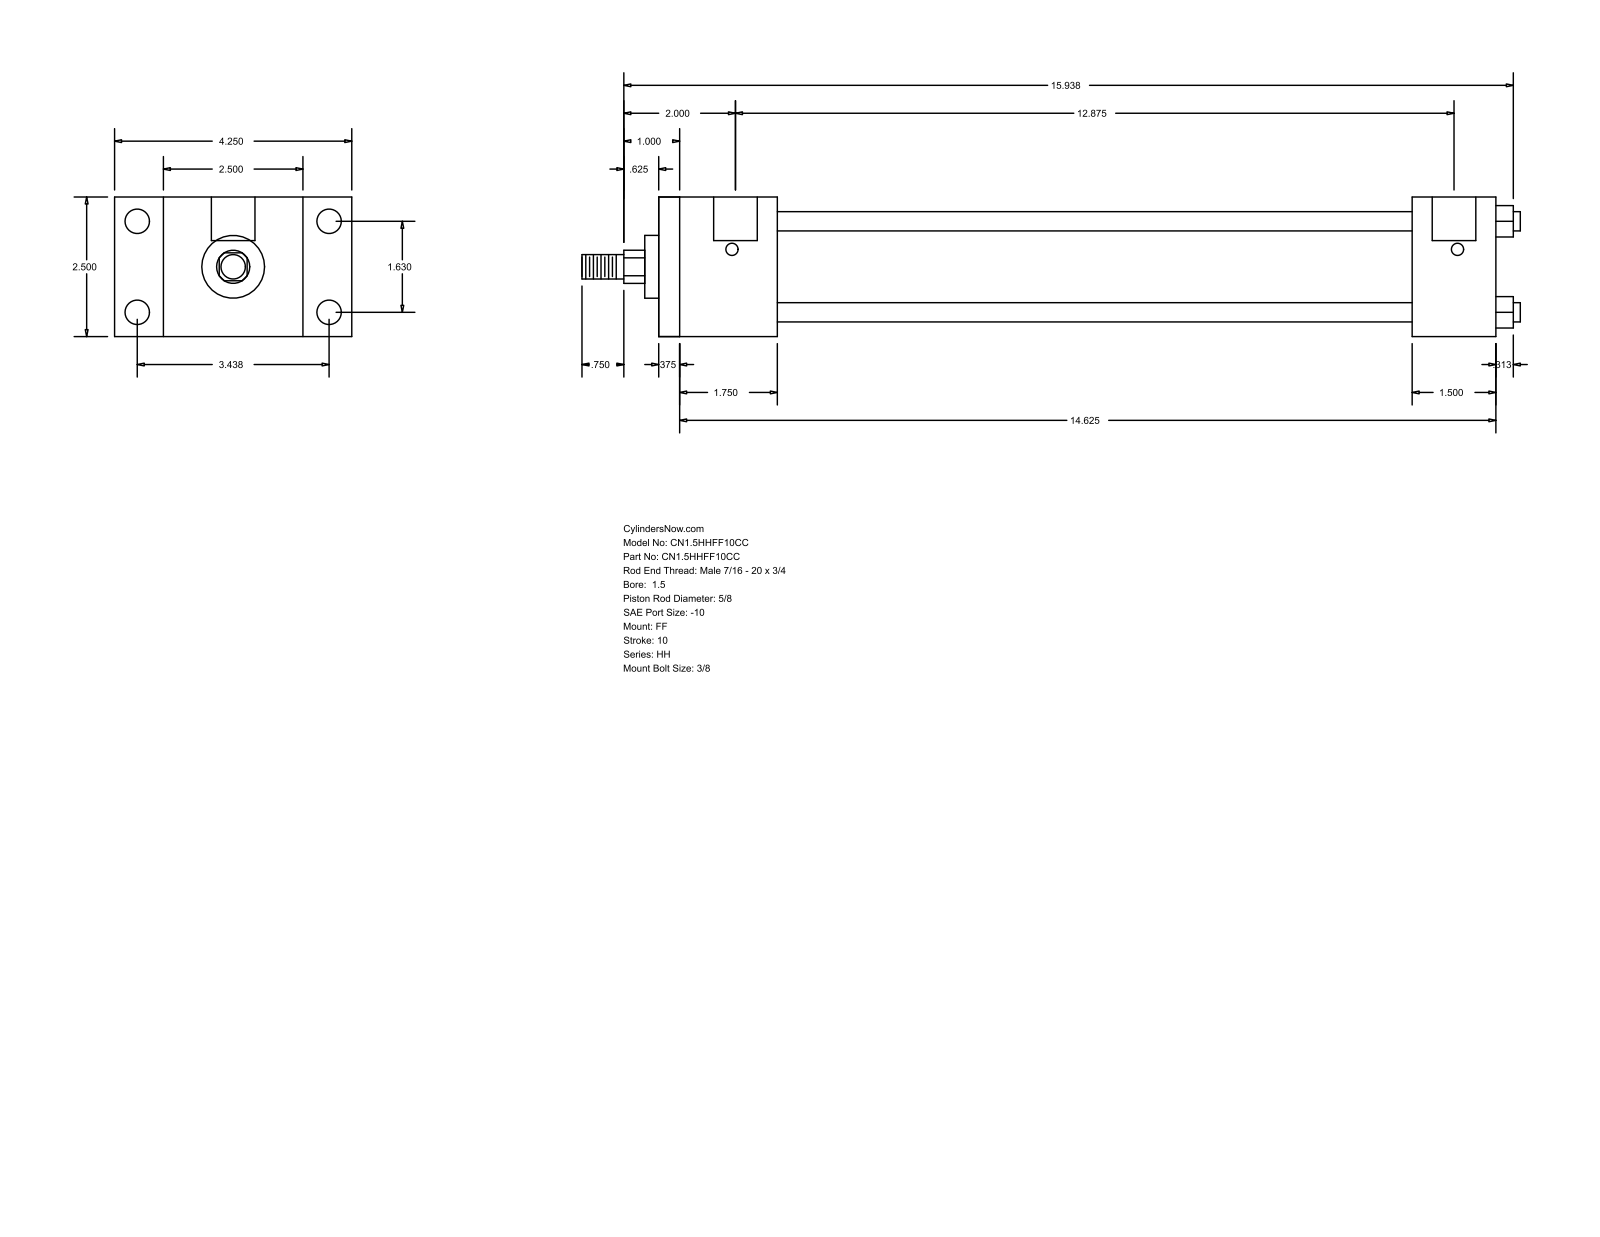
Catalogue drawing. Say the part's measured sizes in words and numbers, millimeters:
The part is named "HH_FF__0150_0.625". Its 3-D file was written by "GSSL Pune (CONFIG_CONTROL_DESIGN)". It is 0 solids with 92 faces: 64 planar, 28 cylindrical and 0 other. Overall it measures 427.04 by 107.95 by 63.5 millimeters. Round holes: 4 of diameter 5.56, 4 of diameter 11.13, 2 of diameter 19.84. Round bosses or shafts: 4 of diameter 8.76, 1 of diameter 44.45, 1 of diameter 28.57, 1 of diameter 15.88, 1 of diameter 11.11. Partial cylindrical surfaces (rounded edges, fillets, slot ends): 1 of radius 7.54. The main face-to-face distances are 63.5, 381, 9.52, 371.48, 44.45, 53.97, 327.03, 342.89, 333.37, 288.92. The hole center spacings are 1.59, 41.4, 87.32, 96.64, 328.61, 330.2, 327.02.
